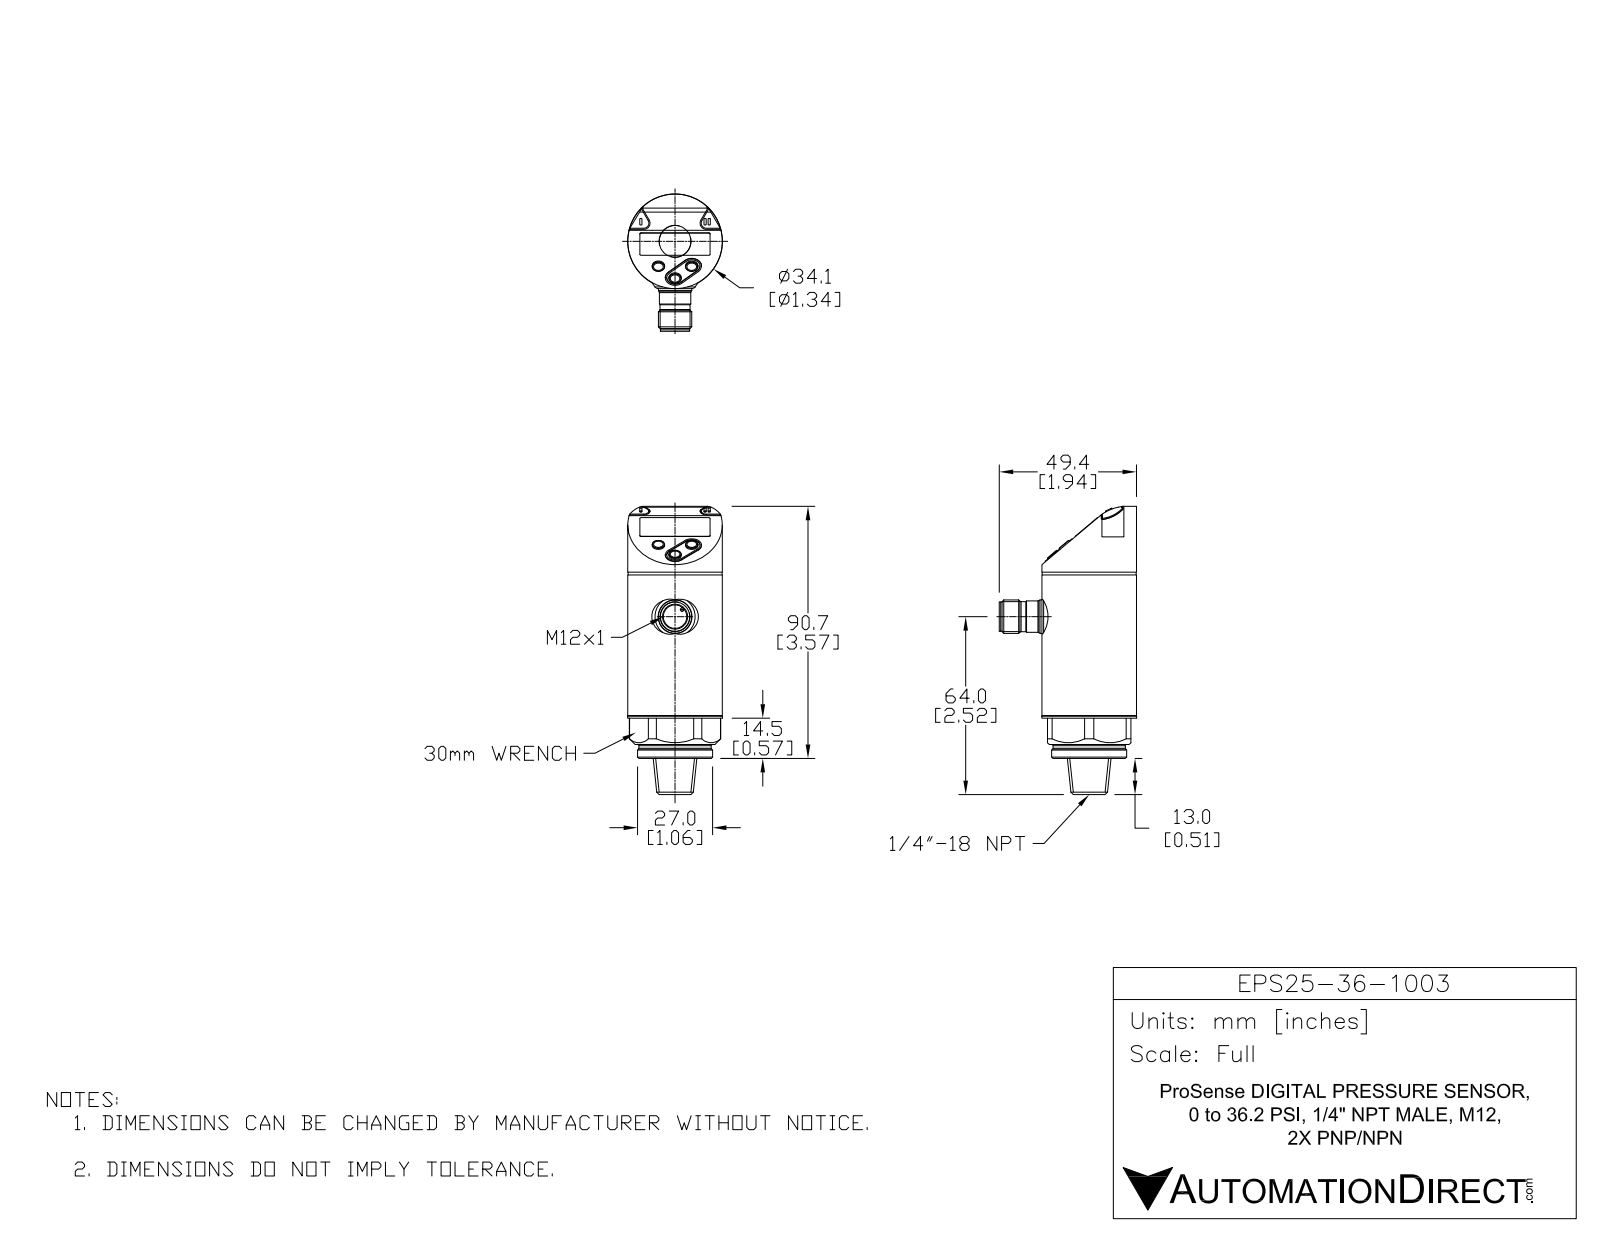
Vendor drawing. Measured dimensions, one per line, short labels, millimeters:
name: EPS25-36-1003
written by: SolidWorks 2016 (AUTOMOTIVE_DESIGN)
unit: mm
bodies: 11 solids, 370 faces (207 planar, 84 cylindrical, 79 other)
size: 103.7 × 49.4 × 34.1
volume: 72 203 mm³; area: 21 365 mm²
holes: 1× ⌀4.2, 1× ⌀8.45
bosses: 4× ⌀1.4, 4× ⌀1, 1× ⌀34.1, 1× ⌀34, 1× ⌀33.8, 1× ⌀27, 1× ⌀26, 1× ⌀12
rounds: 2× R1.8, 2× R2.2, 2× R3, 2× R3.5, 2× R15, 1× R0.61, 1× R6.8, 1× R16.44
face distances: 0.68, 11.5, 12.18, 10.68, 1.5, 10, 2, 2.5, 14, 4
